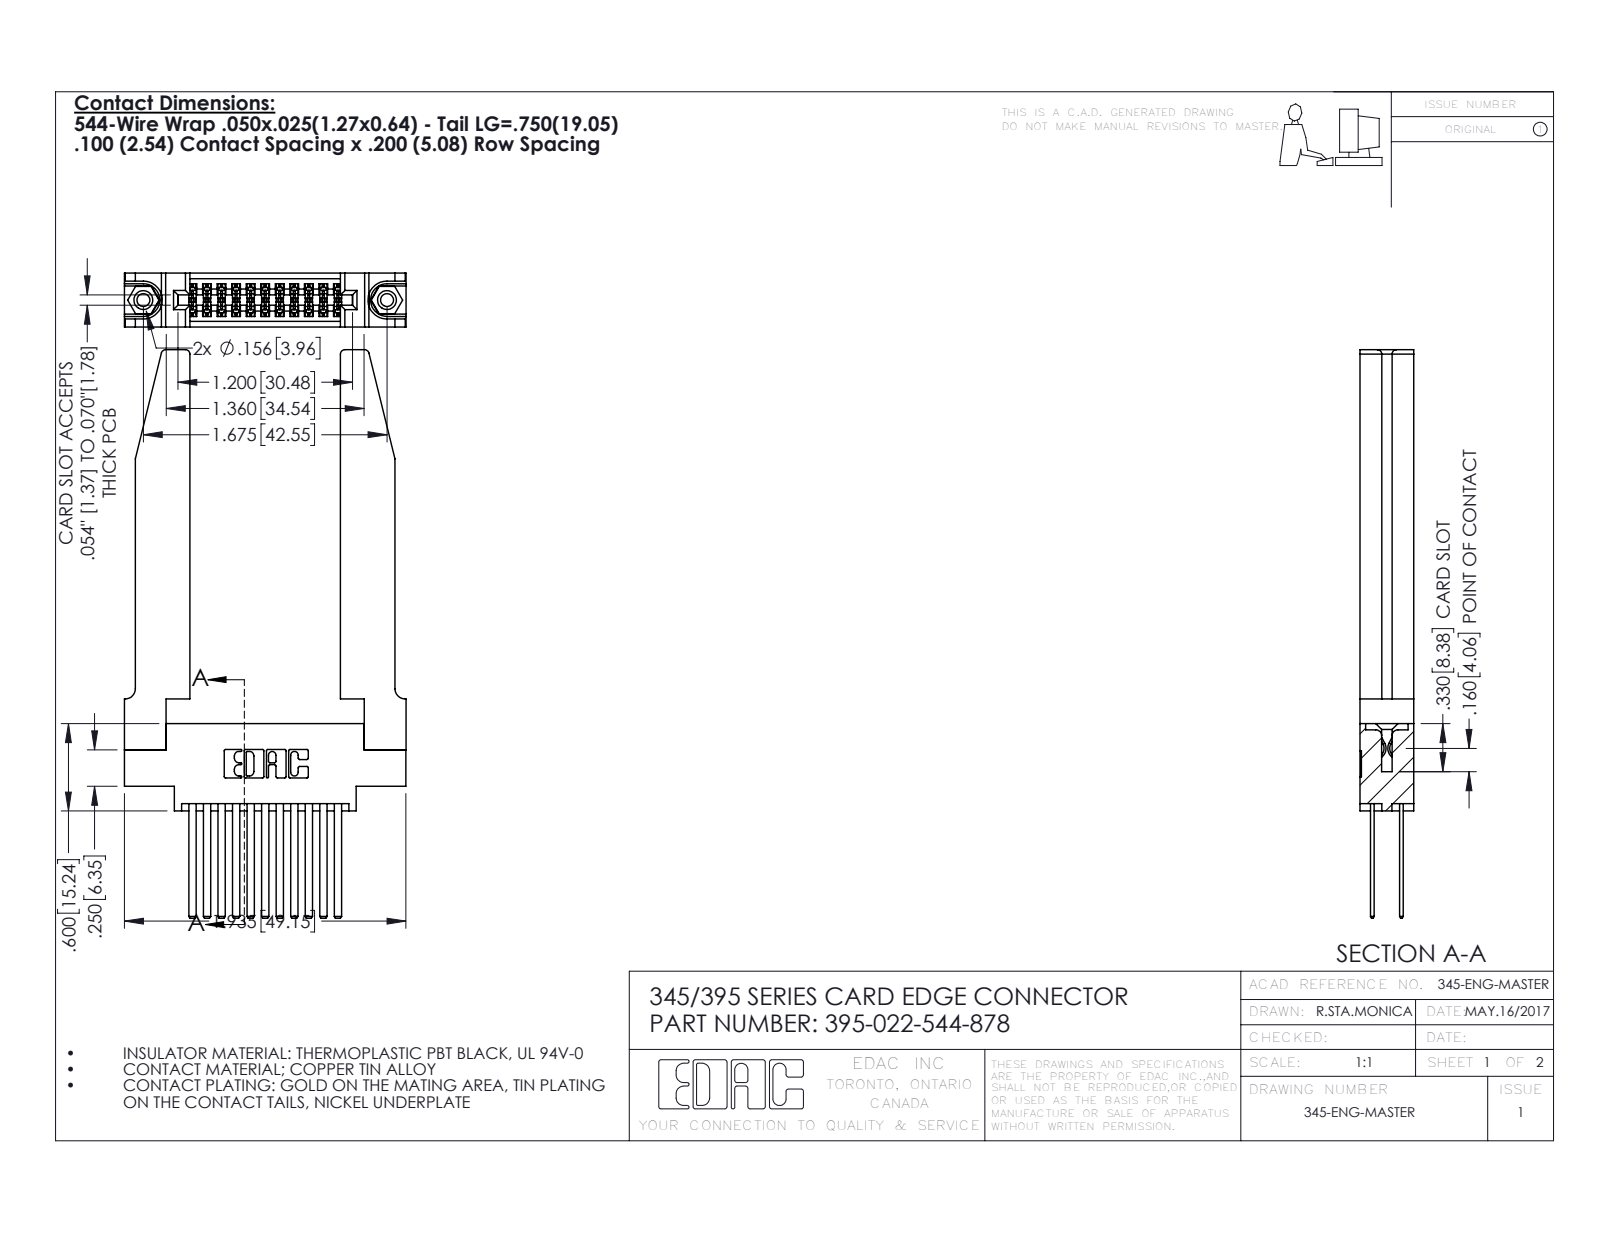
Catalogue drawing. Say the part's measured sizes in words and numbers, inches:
The part is named "345-292-001_345-293-144; 345-250-001_345-250-001-102; 395-022-544-878; 345-220-078_345-220-078 (+1 more)". Its 3-D file was written by "SolidWorks 2016 (CONFIG_CONTROL_DESIGN)". It is 27 solids with 1332 faces: 864 planar, 416 cylindrical and 52 other. Overall it measures 3.907 by 1.936 by 0.37 inches. Its volume is 0.76 cubic inches and its surface area 22.02 square inches. Round holes: 2 of diameter 0.089, 2 of diameter 0.125, 2 of diameter 0.156, 1 of diameter 0.064. Round bosses or shafts: 2 of diameter 0.155. Partial cylindrical surfaces (rounded edges, fillets, slot ends): 33 of radius 0.006, 22 of radius 0.01, 8 of radius 0.03, 6 of radius 0.007, 6 of radius 0.031, 3 of radius 0.026, 2 of radius 0.014, 2 of radius 0.019. The main face-to-face distances are 0.37, 0.072, 0.298, 0.098, 0.272, 0.025, 0.2, 0.225, 0.148, 0.15. The hole center spacings are 0.27, 1.443, 1.675.
